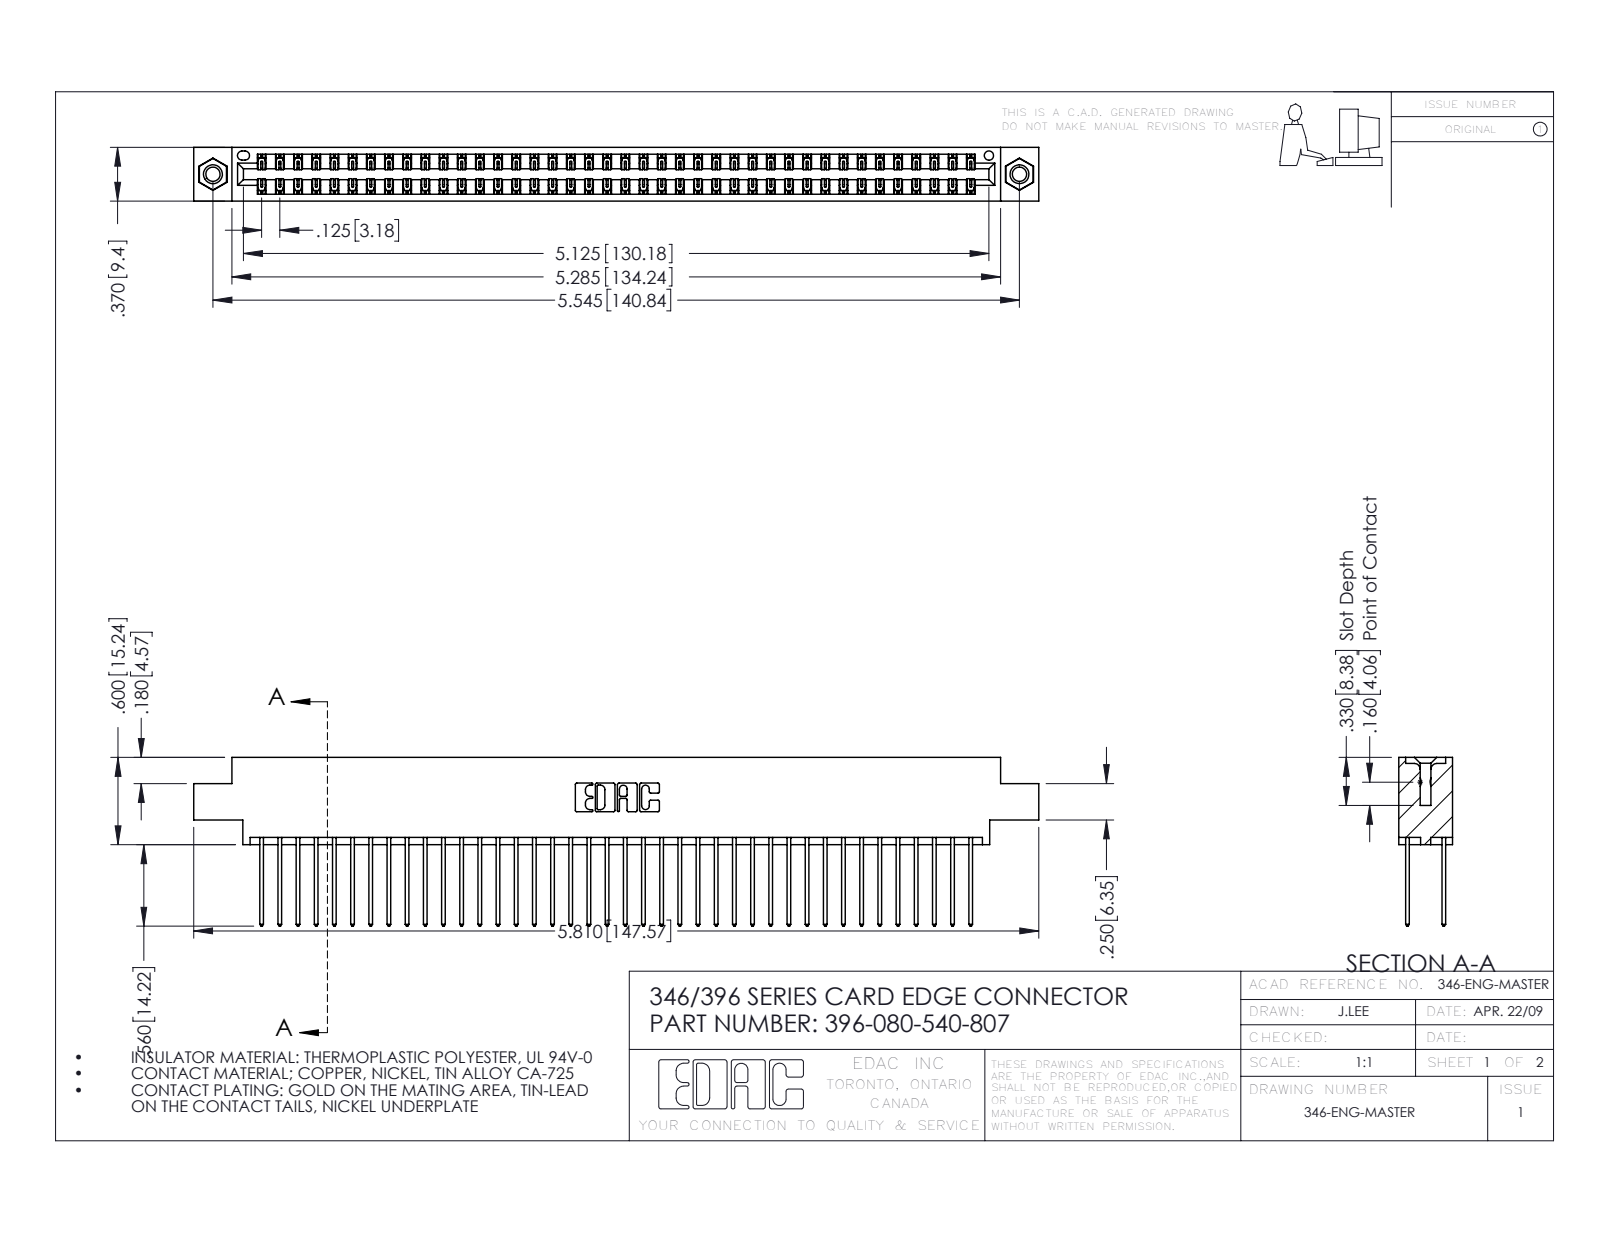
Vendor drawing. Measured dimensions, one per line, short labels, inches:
name: 345-250-001_345-250-005-103; 396-080-540-807; 345-292-001_345-293-140; 346 Part_0.170 Offset - 0.156 Dia-TI
written by: SolidWorks 2016 (CONFIG_CONTROL_DESIGN)
unit: in
bodies: 83 solids, 4346 faces (2912 planar, 1418 cylindrical, 16 other)
size: 5.81 × 1.16 × 0.37
volume: 0.885 in³; area: 33.42 in²
holes: 2× ⌀0.098, 2× ⌀0.125, 2× ⌀0.156, 1× ⌀0.064
bosses: 2× ⌀0.155
rounds: 120× R0.006, 80× R0.01, 22× R0.01, 6× R0.007, 6× R0.031, 3× R0.026, 2× R0.014, 2× R0.022
face distances: 0.048, 0.322, 0.25, 0.072, 0.298, 0.025, 0.37, 0.275, 0.222, 0.148
hole spacings: 0.246, 5.336, 5.545
